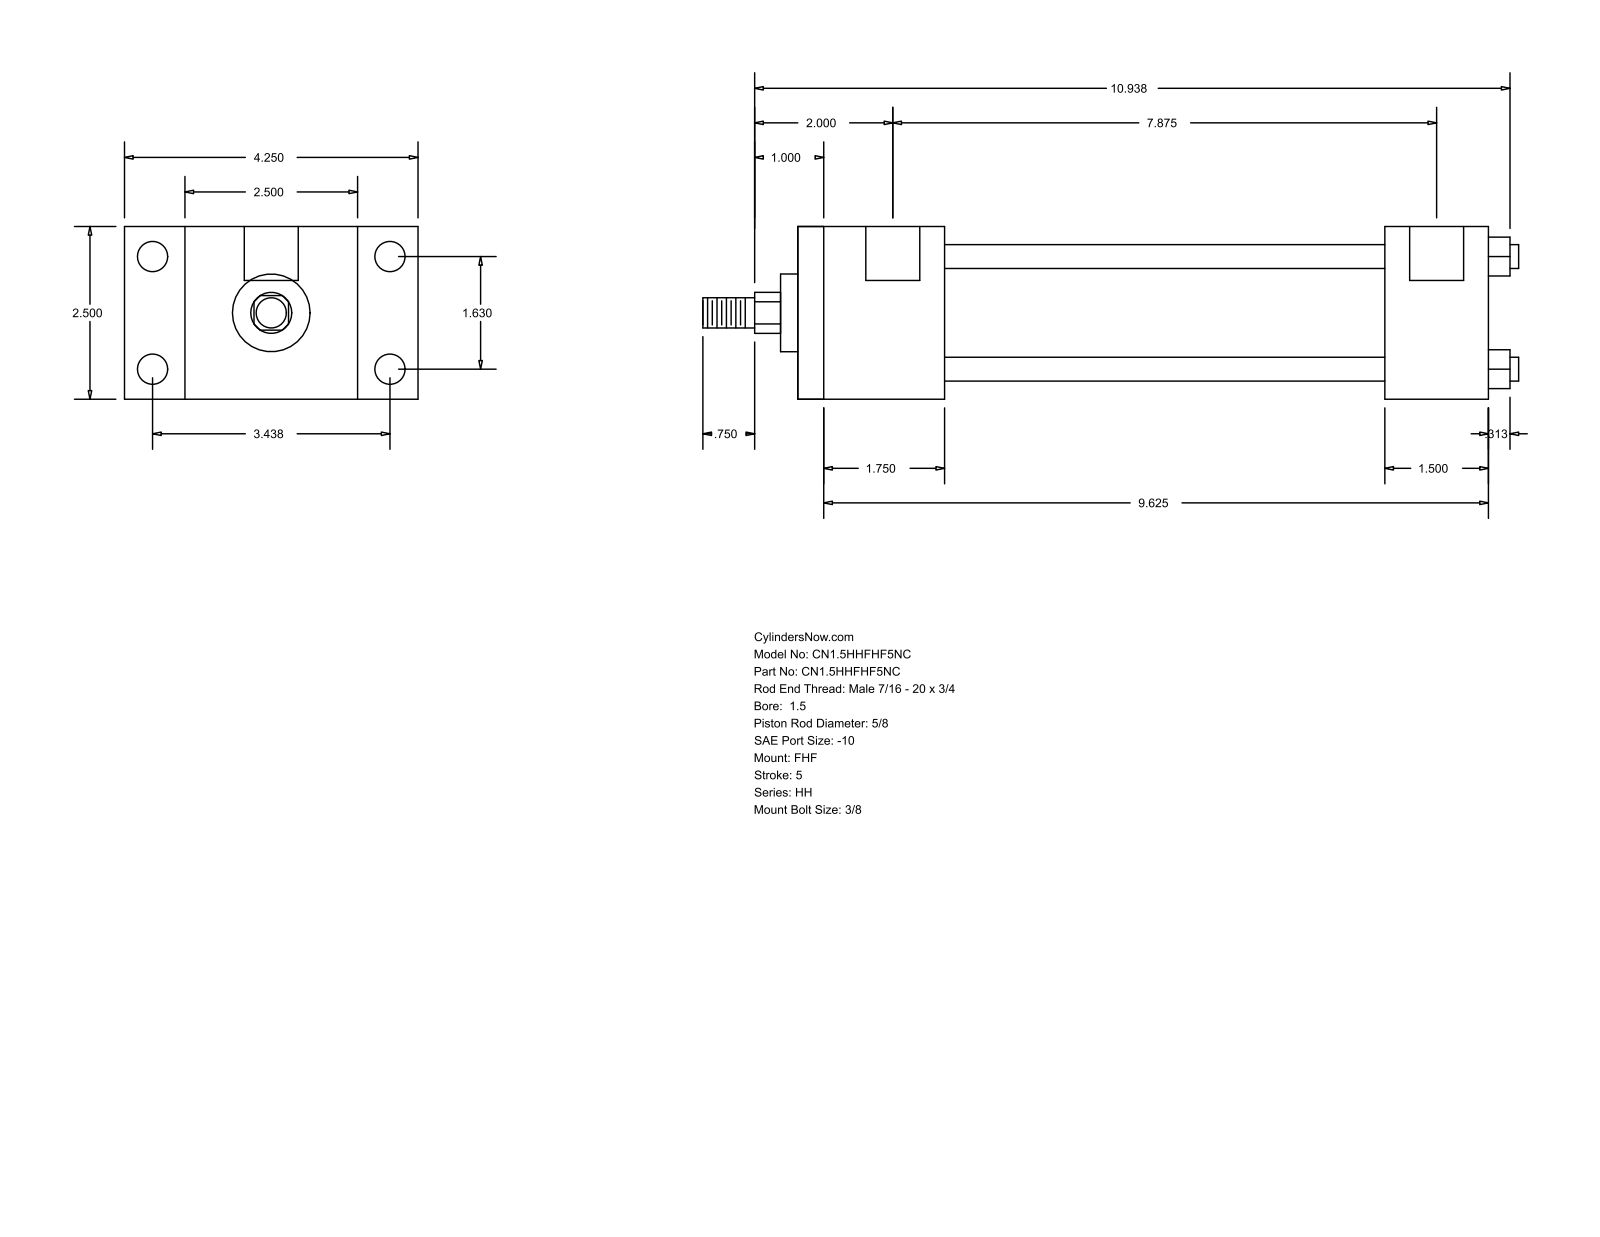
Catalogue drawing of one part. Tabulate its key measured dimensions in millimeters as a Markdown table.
| quantity | value |
| --- | --- |
| part name | HH_FHF__0150_0.625 |
| STEP written by | GSSL Pune (CONFIG_CONTROL_DESIGN) |
| units | millimeters |
| bodies | 0 solids, 88 faces (60 planar, 28 cylindrical, 0 other) |
| overall size | 300.04 × 107.95 × 63.5 |
| round holes (diameter × count) | 5.56 × 4, 11.13 × 4, 19.84 × 2 |
| round bosses / shafts (diameter × count) | 8.76 × 4, 44.45 × 1, 28.57 × 1, 15.88 × 1, 11.11 × 1 |
| partial cylindrical surfaces (radius × count) | 7.54 × 1 |
| main face-to-face distances | 63.5, 22.23, 85.73, 53.97, 107.96, 254, 200.03, 38.1, 215.9, 161.93 |
| hole center spacings | 1.59, 41.4, 87.32, 96.64, 201.61, 203.2, 200.02 |
